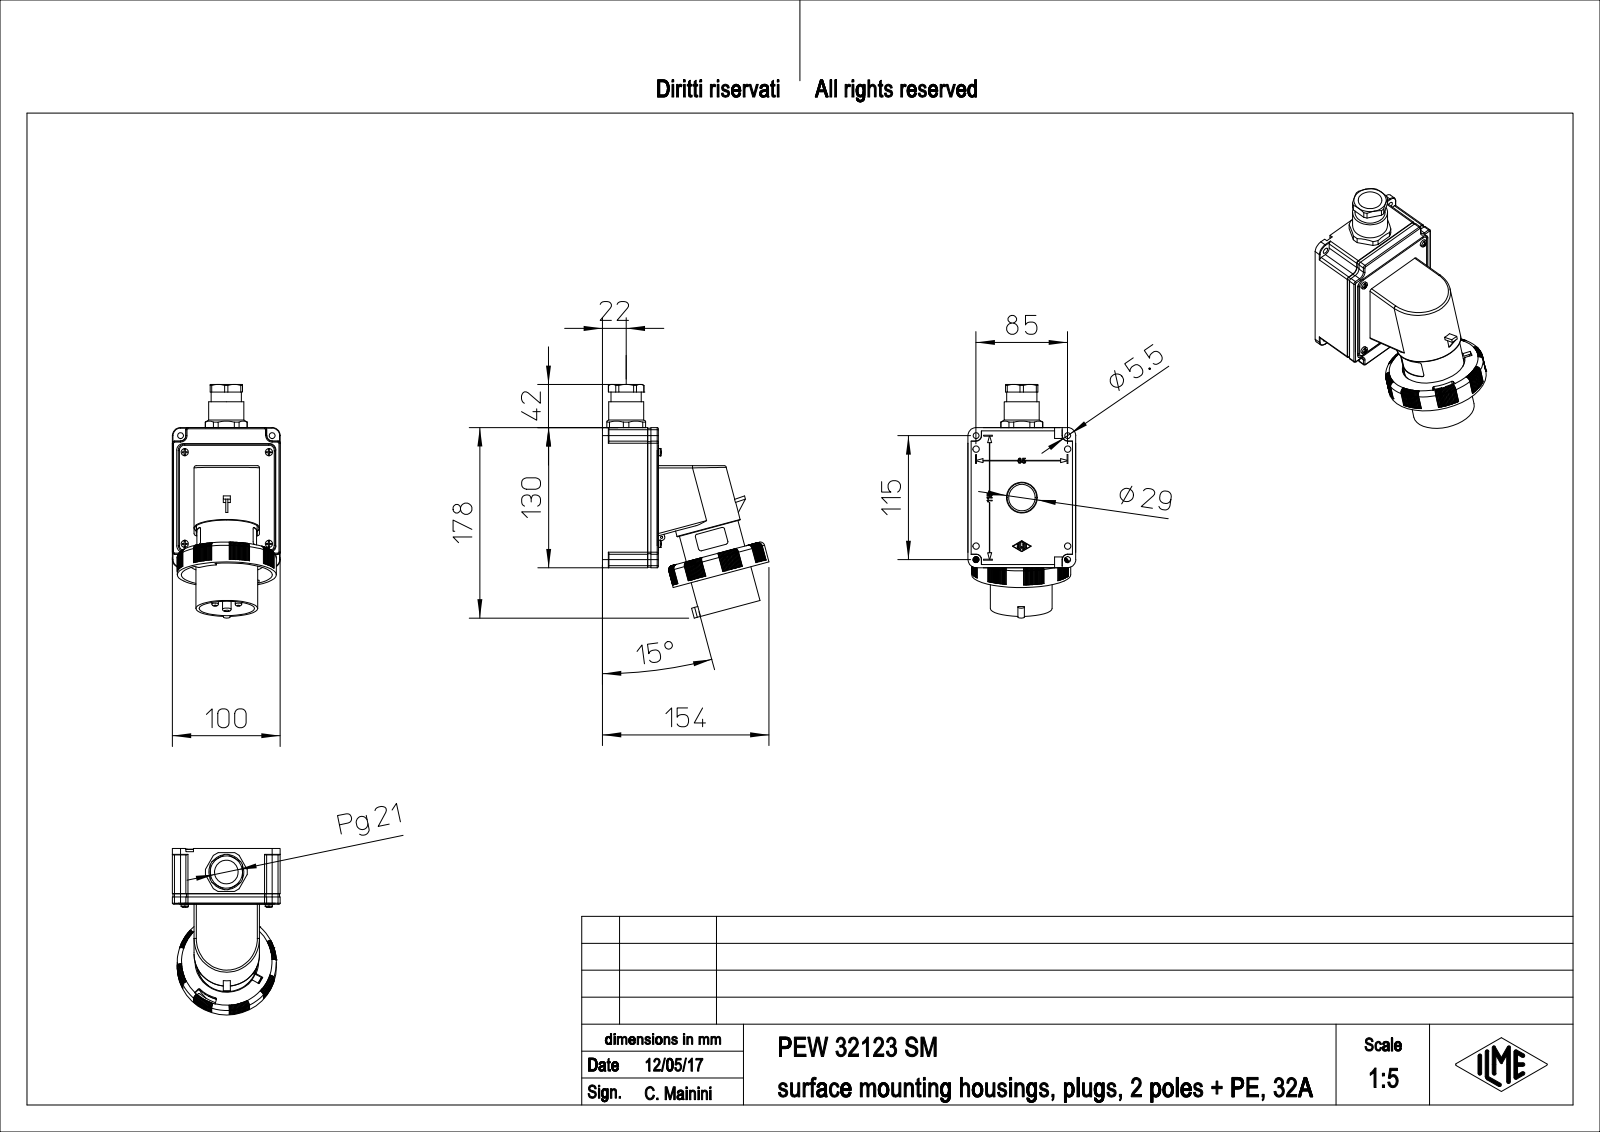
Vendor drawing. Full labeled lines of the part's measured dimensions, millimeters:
Part name (STEP PRODUCT): PEW_32123_SM
STEP written by: PTC Creo Elements/Direct Modeling 19.0E 27-Jun-2016 (C) Parametric Technology GmbH (AUTOMOTIVE_DESIGN)
Units: millimetres
Bodies: 1 solid, 1809 faces (910 planar, 379 cylindrical, 520 other)
Overall size (bounding box): 216.68 × 154.57 × 100
Volume: 971 882 mm³ · Surface area: 156 731 mm²
Round holes (diameter × count): ⌀5.5 ×8, ⌀6 ×4, ⌀4 ×2, ⌀4.2 ×2, ⌀6.1 ×2, ⌀28.6 ×2, ⌀2 ×1, ⌀22 ×1, ⌀84.5 ×1
Round bosses / shafts (diameter × count): ⌀6.7 ×6, ⌀6 ×2, ⌀3 ×2, ⌀92 ×1, ⌀70 ×1, ⌀60.7 ×1, ⌀57.3 ×1, ⌀56.2 ×1
Partial cylindrical surfaces — rounded edges, fillets, slot ends (radius × count): R3.6 ×136, R0.5 ×18, R1 ×10, R2 ×10, R41.53 ×10, R1.5 ×8, R6 ×8, R0.3 ×4
Main face-to-face distances: 2, 4.5, 44.3, 50.8, 6.5, 46.3, 3, 100, 94.65, 6.85
Hole centre spacings: 12.5, 85, 61.9, 71.5, 85.91, 102.5, 133.16, 21
